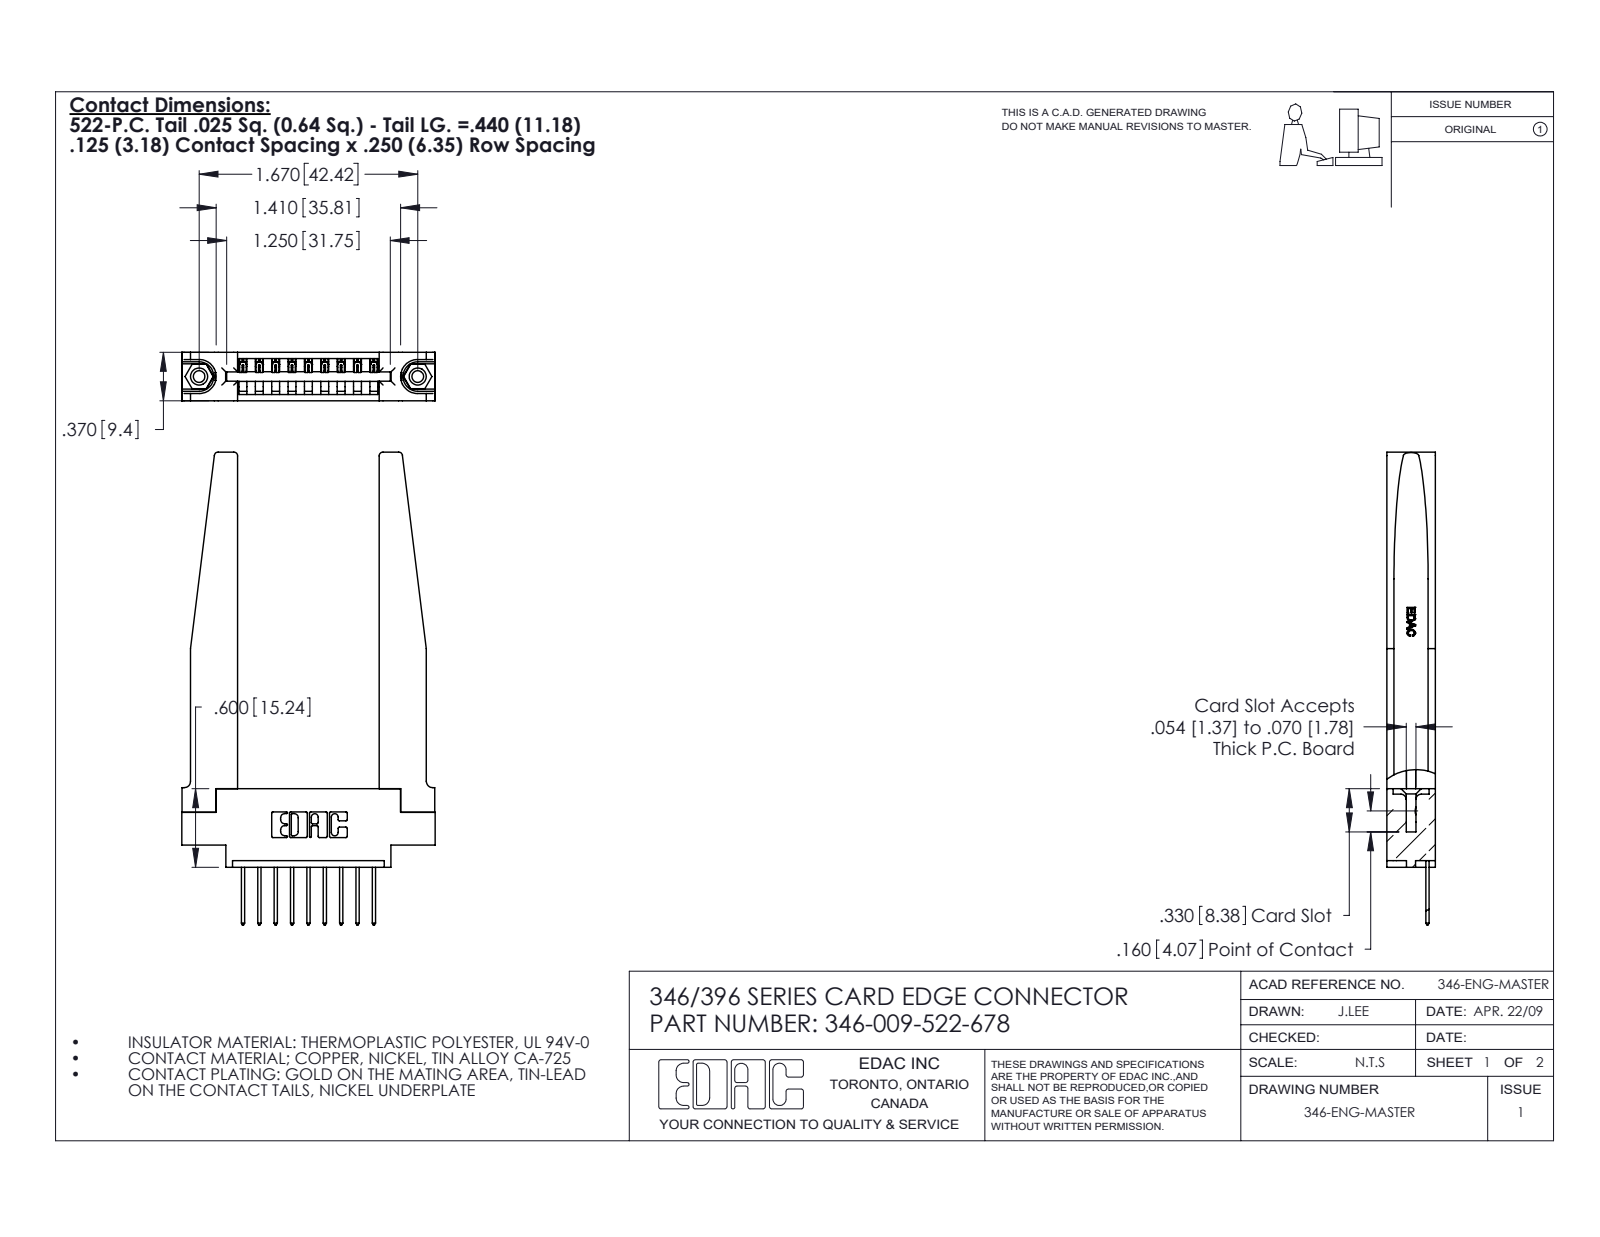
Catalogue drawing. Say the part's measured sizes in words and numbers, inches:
The part is named "345-292-001_345-293-122; 346-009-522-678; 345-250-001_345-250-001-102; 346 Part_0.170 Offset - 0.156 Dia-TH (+1 more)". Its 3-D file was written by "SolidWorks 2020 (CONFIG_CONTROL_DESIGN)". It is 14 solids with 896 faces: 596 planar, 248 cylindrical and 52 other. Overall it measures 3.61 by 1.935 by 0.37 inches. Its volume is 0.684 cubic inches and its surface area 18.28 square inches. Round holes: 2 of diameter 0.089, 2 of diameter 0.125, 2 of diameter 0.156, 1 of diameter 0.064. Round bosses or shafts: 2 of diameter 0.155. Partial cylindrical surfaces (rounded edges, fillets, slot ends): 22 of radius 0.01, 18 of radius 0.006, 18 of radius 0.01, 8 of radius 0.03, 6 of radius 0.007, 6 of radius 0.031, 3 of radius 0.026, 2 of radius 0.031. The main face-to-face distances are 0.37, 0.15, 0.072, 0.148, 0.22, 0.25, 0.048, 0.322, 0.102, 0.173. The hole center spacings are 0.246, 1.465, 1.67.
